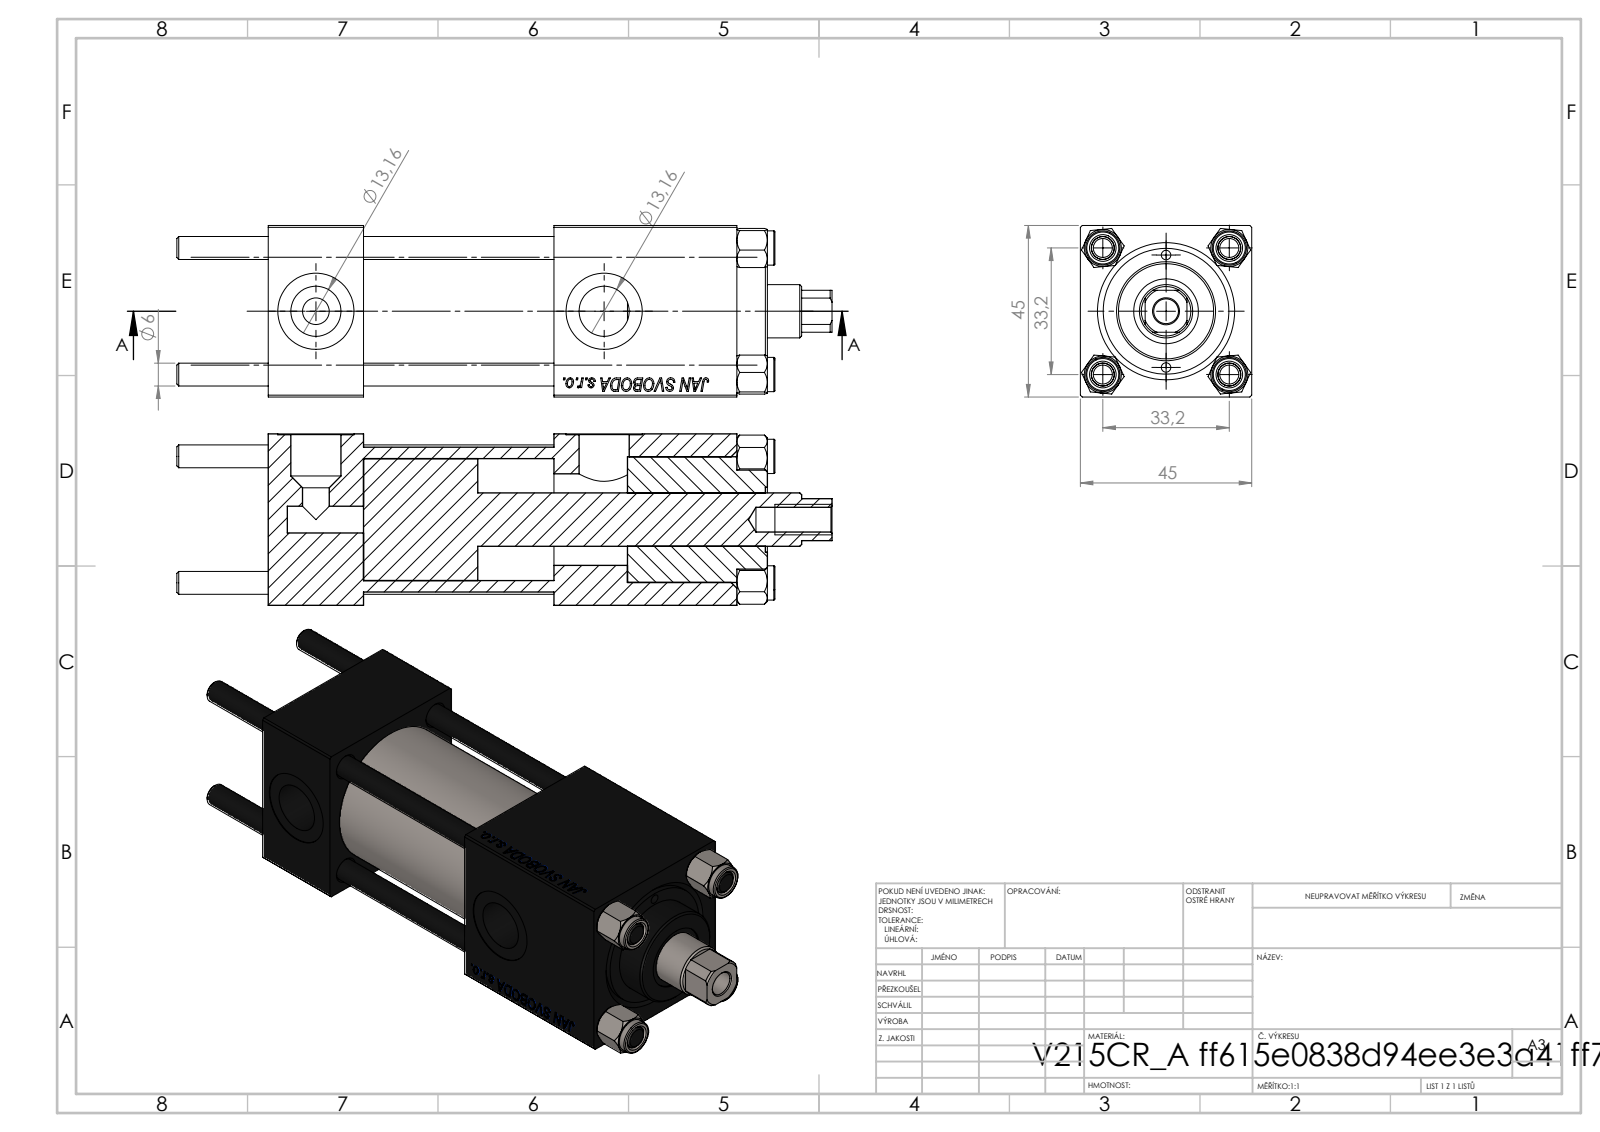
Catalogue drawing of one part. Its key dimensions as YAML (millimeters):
part_name: "V215CR_BODY_A; CR025_012_A_0_G_A_G_M_020_+#_##_TYCINKA; V215_VC_A; V215CR_VCP (+1 more)"
step_written_by: "SolidWorks 2019 (CONFIG_CONTROL_DESIGN)"
units: millimeters
bodies: {solids: 11, faces: 1138, planar: 519, cylindrical: 83, other: 536}
overall_size: [172, 45, 45]
volume: 198181
surface_area: 72886
round_holes:
  - {diameter: 6, count: 4}
  - {diameter: 2.5, count: 2}
  - {diameter: 7, count: 2}
  - {diameter: 13.16, count: 2}
  - {diameter: 20, count: 2}
  - {diameter: 6.5, count: 1}
  - {diameter: 14, count: 1}
  - {diameter: 17, count: 1}
  - {diameter: 24, count: 1}
  - {diameter: 32, count: 1}
  - {diameter: 33, count: 1}
round_bosses_or_shafts:
  - {diameter: 9, count: 4}
  - {diameter: 38, count: 1}
  - {diameter: 26, count: 1}
partial_cylinders:
  - {radius: 6.5, count: 1}
face_to_face_distances: [45, 25, 123, 98, 50, 75, 48, 94.3, 69.3, 19.3]
hole_center_spacings: [16.7, 23.48, 33.2, 35.47, 14.75, 46.95, 29.5, 75.66]
